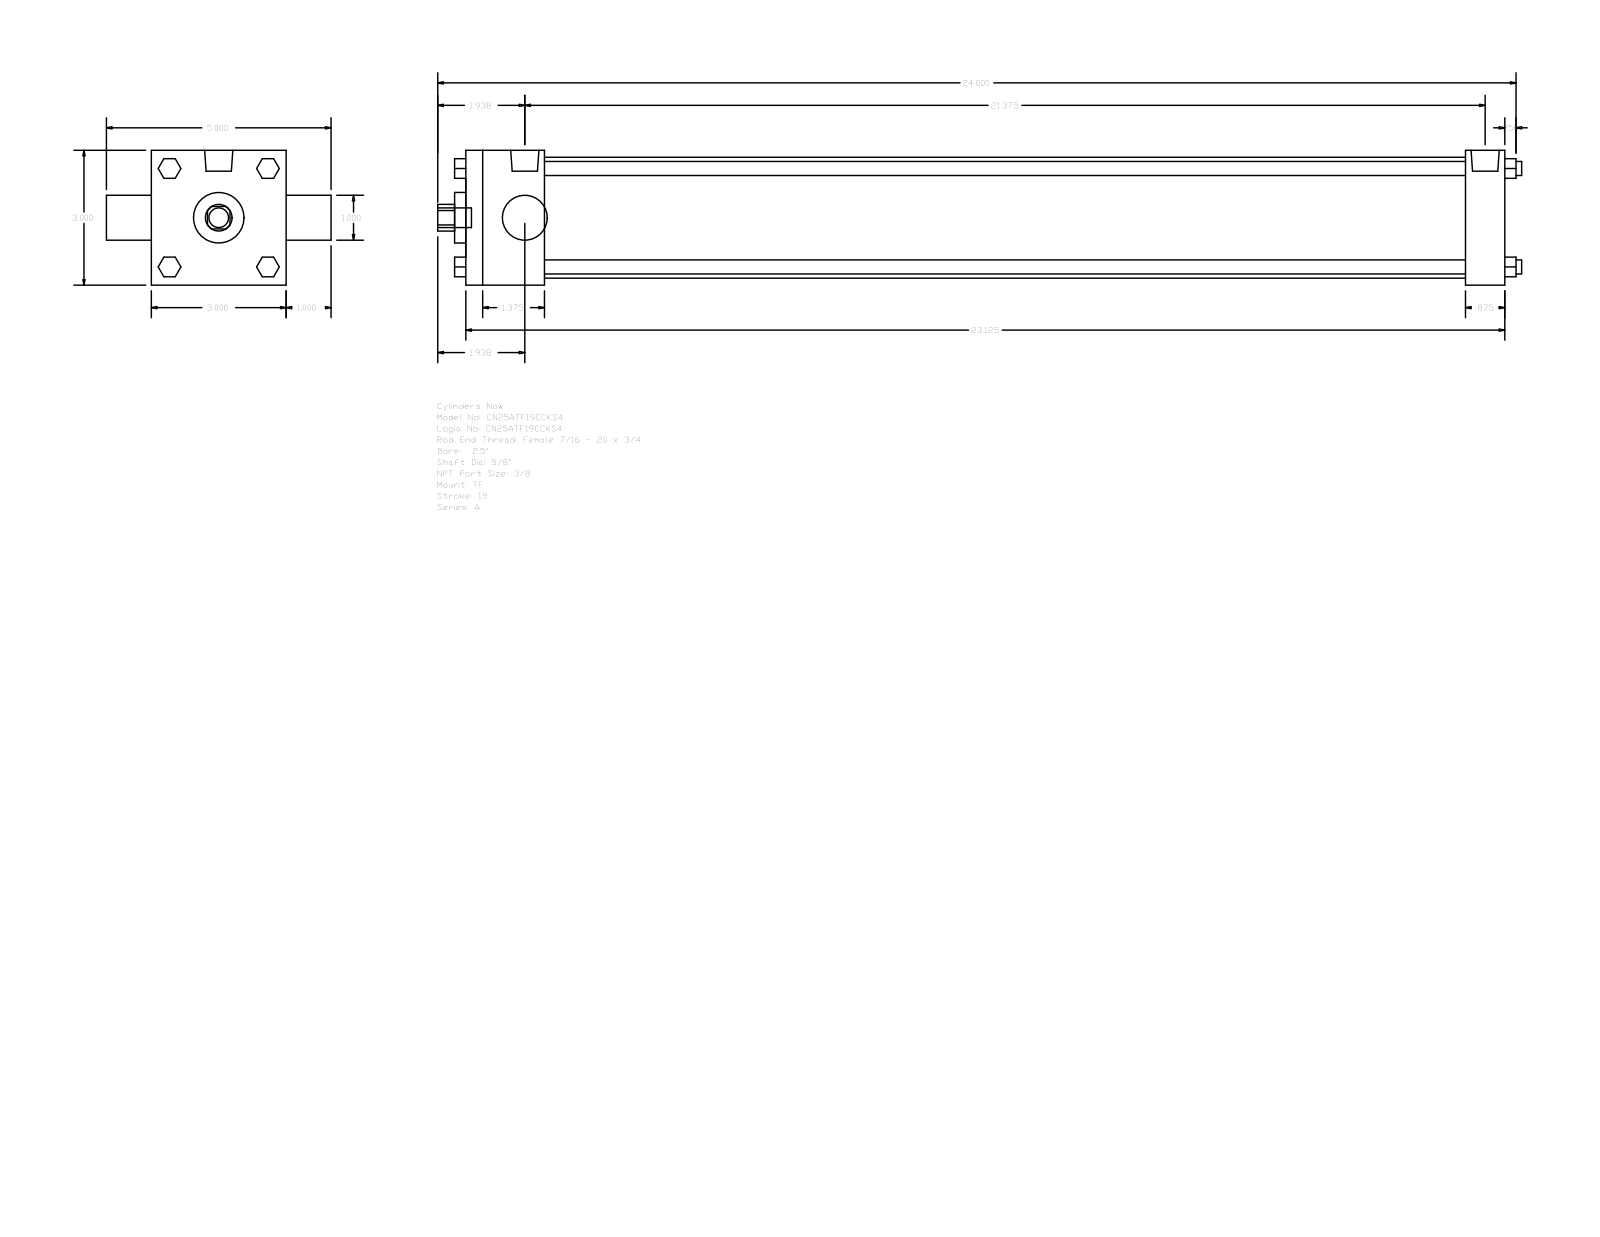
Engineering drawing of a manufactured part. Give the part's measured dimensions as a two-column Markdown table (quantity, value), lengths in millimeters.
| quantity | value |
| --- | --- |
| part name | A_TF__0250_0.625 |
| STEP written by | GSSL Pune (CONFIG_CONTROL_DESIGN) |
| units | millimeters |
| bodies | 0 solids, 120 faces (92 planar, 28 cylindrical, 0 other) |
| overall size | 612.77 × 127 × 76.2 |
| round holes (diameter × count) | 15.88 × 1, 25.4 × 1, 28.57 × 1, 68.33 × 1 |
| round bosses / shafts (diameter × count) | 7.94 × 4, 5.56 × 3, 15.93 × 2, 11.11 × 1 |
| partial cylindrical surfaces (radius × count) | 7.54 × 1 |
| main face-to-face distances | 76.2, 587.37, 44.45, 565.14, 520.69, 542.92, 22.23, 25.4, 101.6, 593.72 |
